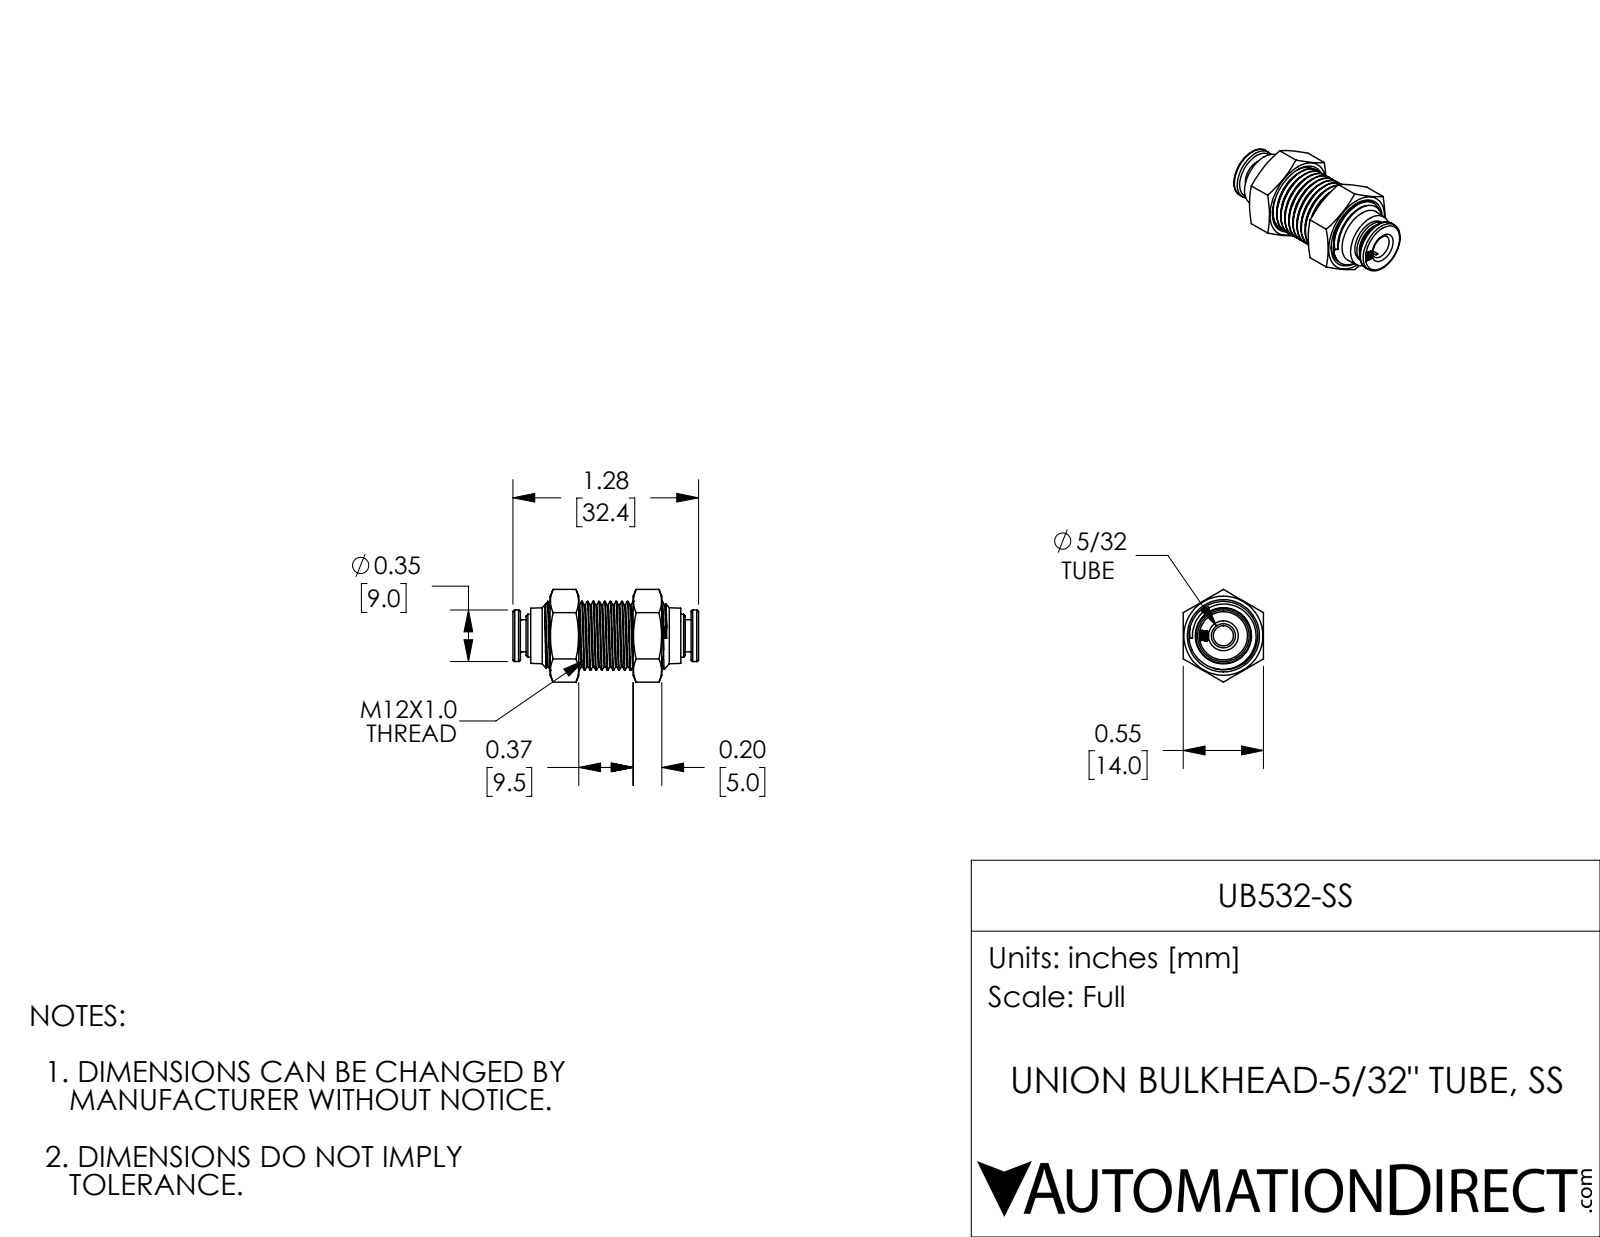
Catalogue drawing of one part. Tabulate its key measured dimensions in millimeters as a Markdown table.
| quantity | value |
| --- | --- |
| part name | UB532-SS |
| STEP written by | SolidWorks 2017 (AUTOMOTIVE_DESIGN) |
| units | millimeters |
| bodies | 1 solid, 314 faces (87 planar, 106 cylindrical, 121 other) |
| overall size | 32.4 × 16.2 × 14 |
| volume | 2 980 mm³ |
| surface area | 2 803 mm² |
| round holes (diameter × count) | 3.5 × 1, 4.2 × 1, 11 × 1 |
| round bosses / shafts (diameter × count) | 12 × 1, 10.8 × 1, 9 × 1, 7.5 × 1, 5.6 × 1 |
| partial cylindrical surfaces (radius × count) | 0.8 × 2, 0.8 × 2 |
| main face-to-face distances | 14, 1.3, 31.1, 3.1, 29.3, 1.8, 28, 5, 14.5, 32.4 |
